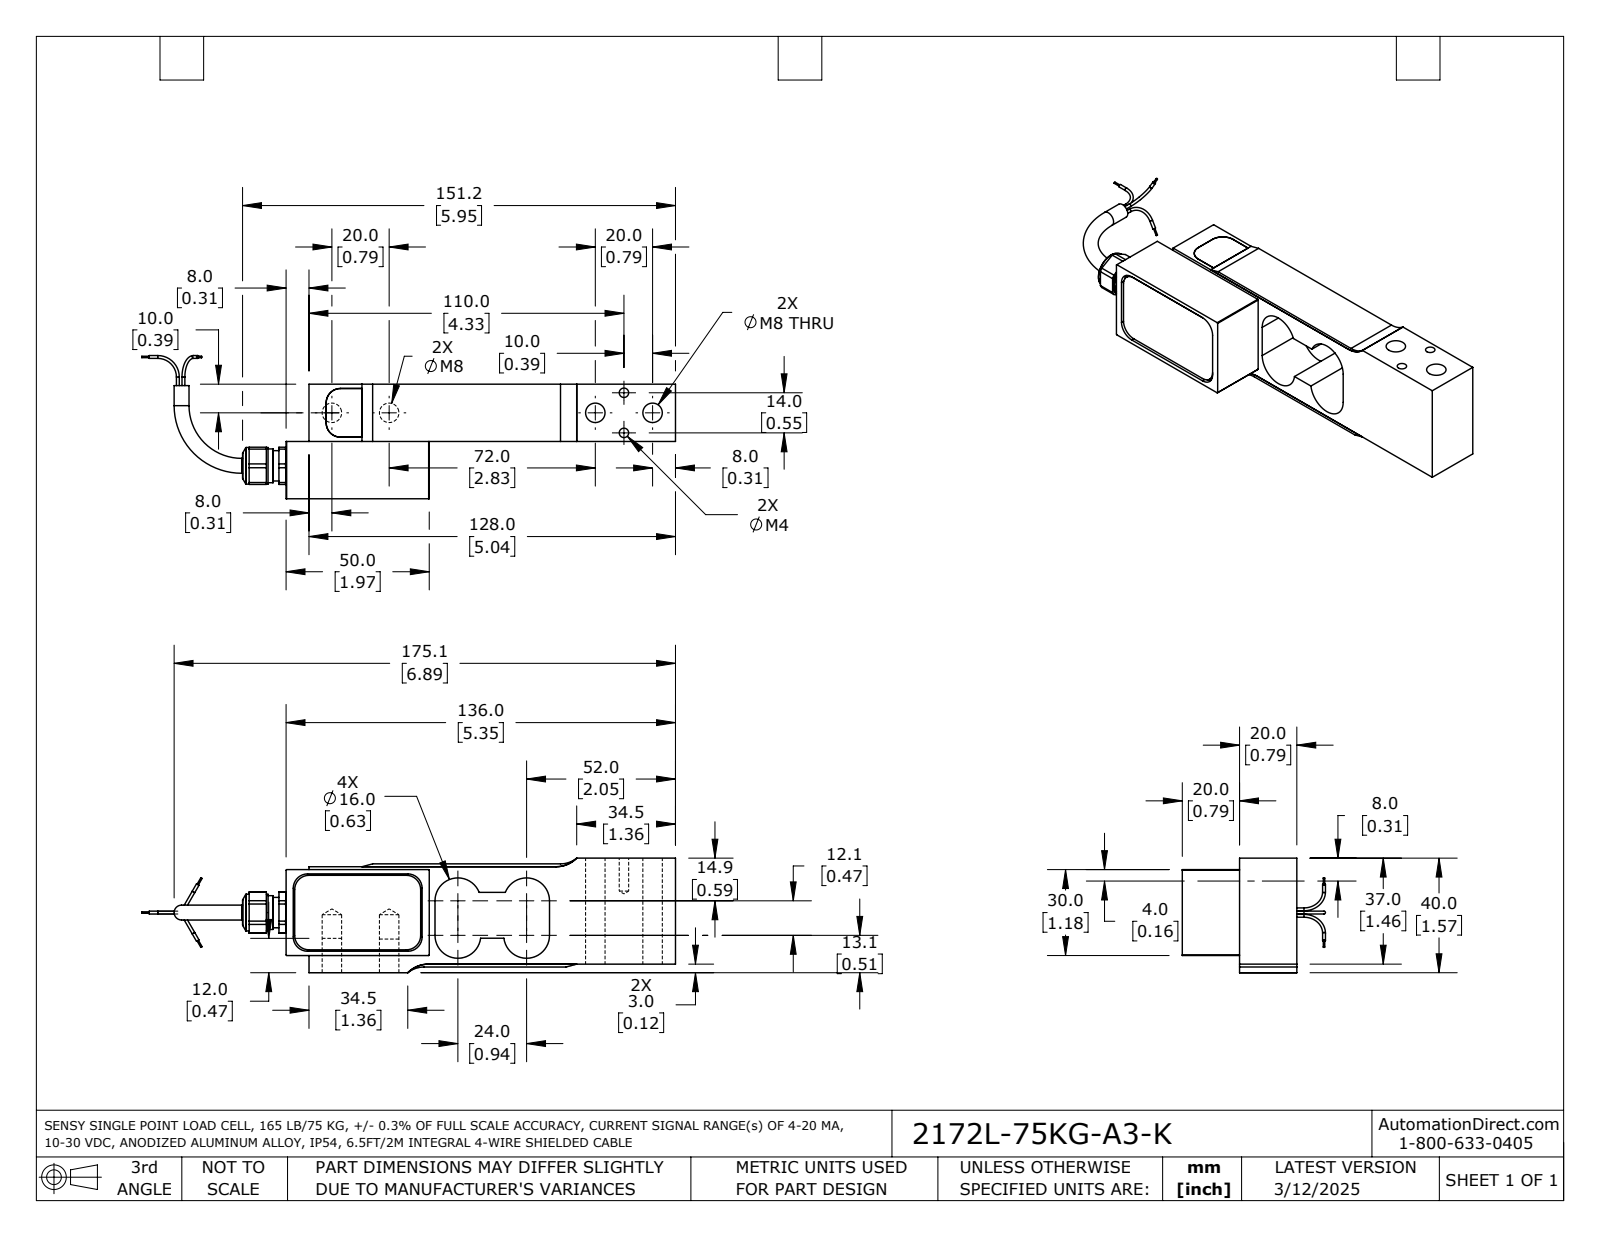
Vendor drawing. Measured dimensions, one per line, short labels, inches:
name: 2172L-75KG-A3-K
written by: SolidWorks 2024 (AUTOMOTIVE_DESIGN)
unit: in
bodies: 12 solids, 282 faces (102 planar, 120 cylindrical, 60 other)
size: 7.339 × 1.969 × 1.575
volume: 5.389 in³; area: 63.88 in²
holes: 4× ⌀0.268, 3× ⌀0.087, 2× ⌀0.063, 2× ⌀0.13, 2× ⌀0.177, 1× ⌀0.157, 1× ⌀0.236, 1× ⌀0.24, 1× ⌀0.244, 1× ⌀0.335, 1× ⌀0.439
bosses: 6× ⌀0.039, 3× ⌀0.02, 2× ⌀0.205, 1× ⌀0.504, 1× ⌀0.464, 1× ⌀0.433, 1× ⌀0.417, 1× ⌀0.394
rounds: 12× R0.197, 4× R0.157, 4× R0.315, 2× R0.354, 2× R0.394, 1× R0.281
face distances: 0.039, 0.787, 0.118, 1.339, 0.157, 0.236, 0.079, 1.181, 1.378, 1.22
hole spacings: 0.481, 0.394, 0.412, 0.74, 0.787, 3.24, 3.622, 4.025
